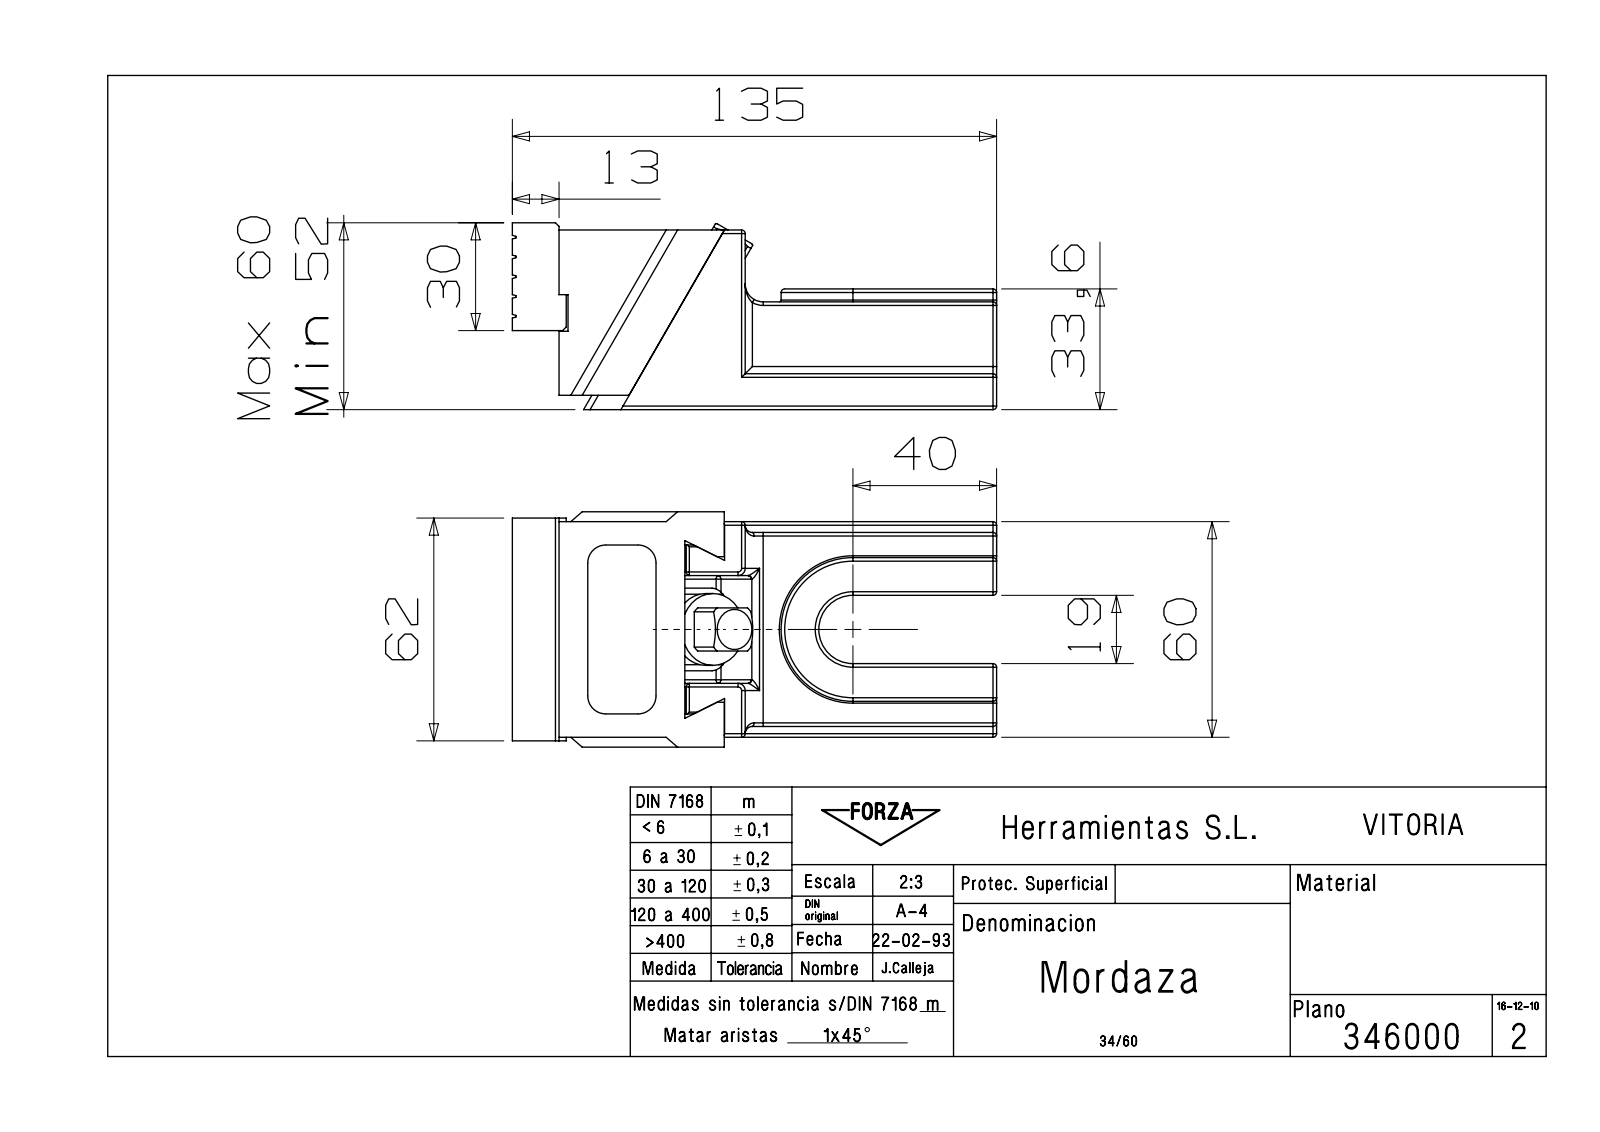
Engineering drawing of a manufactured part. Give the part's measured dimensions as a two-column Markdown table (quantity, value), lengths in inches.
| quantity | value |
| --- | --- |
| part name | 34_60_Mordaza |
| STEP written by | SIEMENS PLM Software NX 1969 (AP203_CONFIGURATION_CONTROLLED_3D_DESIGN_OF_MECHANICAL_PARTS_AND_ASSEMBLIES_MIM_LF) |
| units | inches |
| bodies | 8 solids, 336 faces (155 planar, 117 cylindrical, 64 other) |
| overall size | 5.308 × 2.579 × 2.047 |
| volume | 15.08 in³ |
| surface area | 92.69 in² |
| round holes (diameter × count) | 0.079 × 2, 0.275 × 2, 0.335 × 2, 0.551 × 2, 0.433 × 1, 0.453 × 1, 0.571 × 1, 0.602 × 1 |
| round bosses / shafts (diameter × count) | 0.472 × 3, 0.307 × 2, 0.787 × 1, 0.722 × 1, 0.591 × 1, 0.563 × 1, 0.551 × 1, 0.432 × 1 |
| partial cylindrical surfaces (radius × count) | 0.039 × 46, 0.02 × 11, 0.079 × 7, 0.138 × 5, 0.197 × 5, 0.03 × 2, 0.305 × 1, 0.374 × 1 |
| main face-to-face distances | 0.118, 0.157, 0.748, 1.811, 1.181, 0.689, 0.807, 1.555, 0.472, 1.772 |
| hole center spacings | 0.354, 0.365, 0.2, 1.575 |
